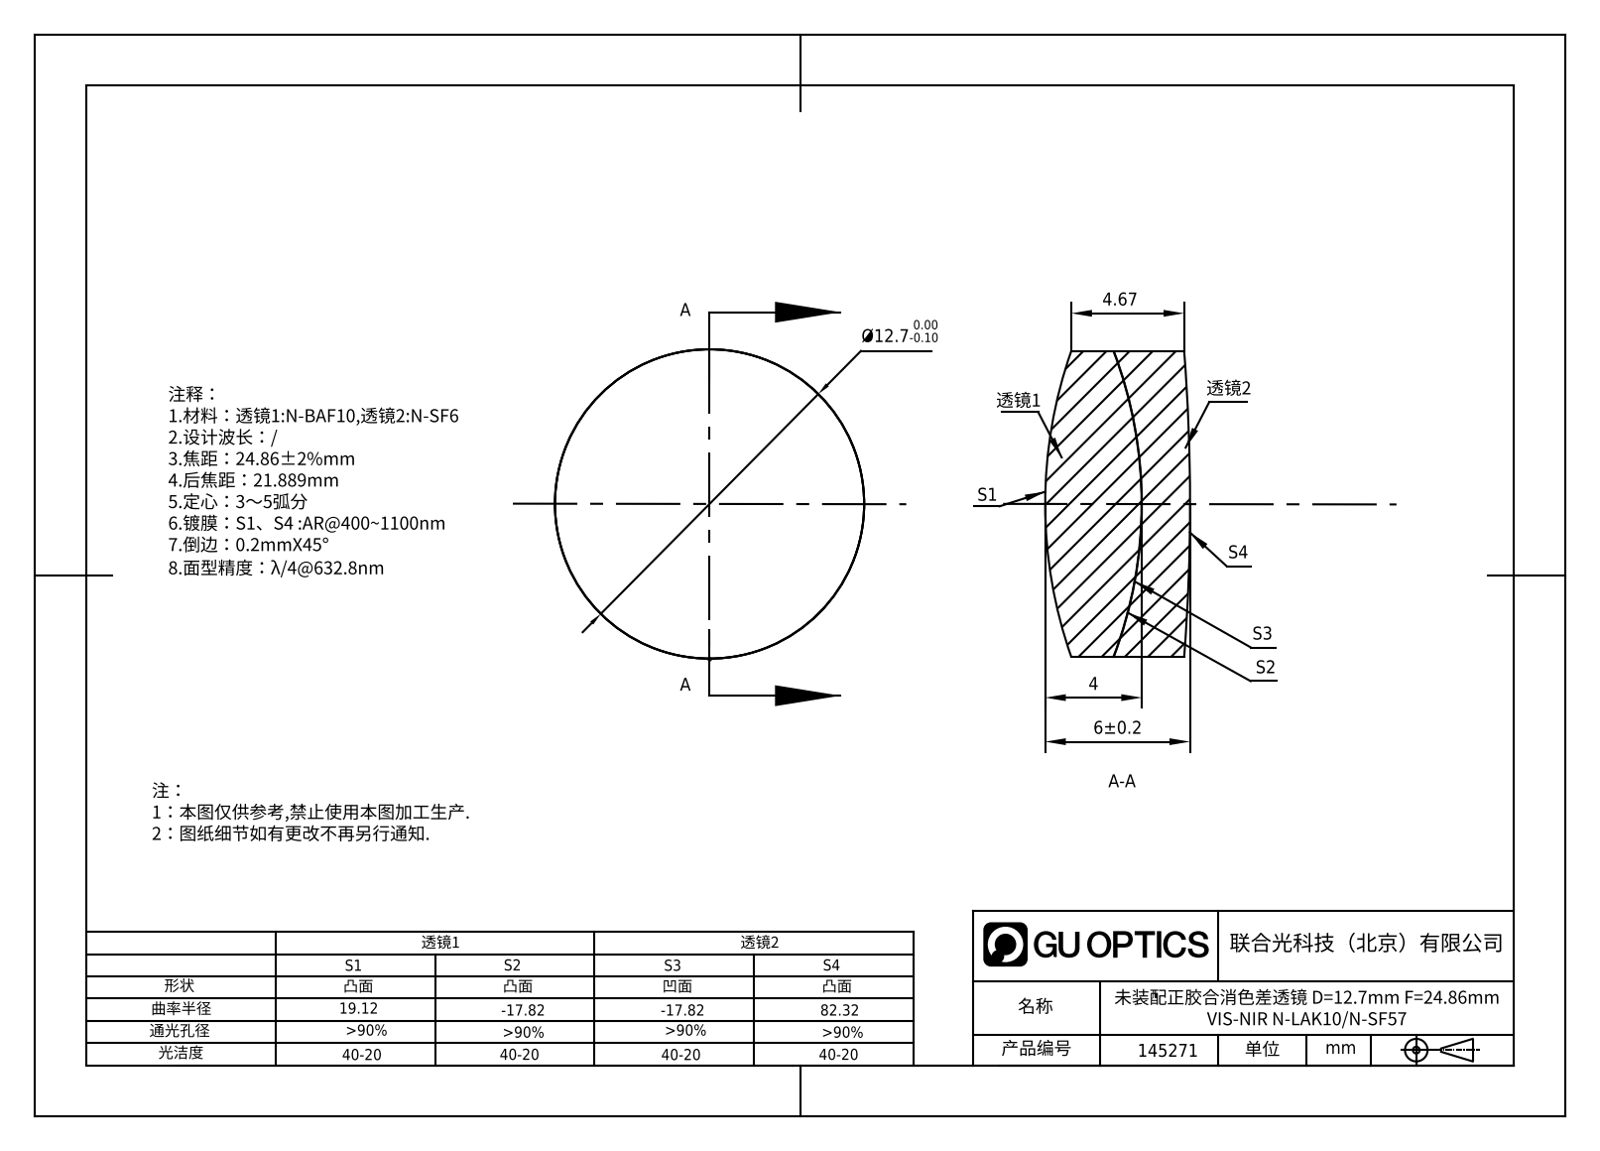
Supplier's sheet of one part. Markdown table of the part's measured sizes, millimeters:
| quantity | value |
| --- | --- |
| part name | 145271 |
| STEP written by | SolidWorks 2020 (CONFIG_CONTROL_DESIGN) |
| units | millimeters |
| bodies | 2 solids, 12 faces (0 planar, 4 cylindrical, 8 other) |
| overall size | 12.71 × 12.7 × 6.01 |
| volume | 676 mm³ |
| surface area | 705 mm² |
| round bosses / shafts (diameter × count) | 12.7 × 2 |
